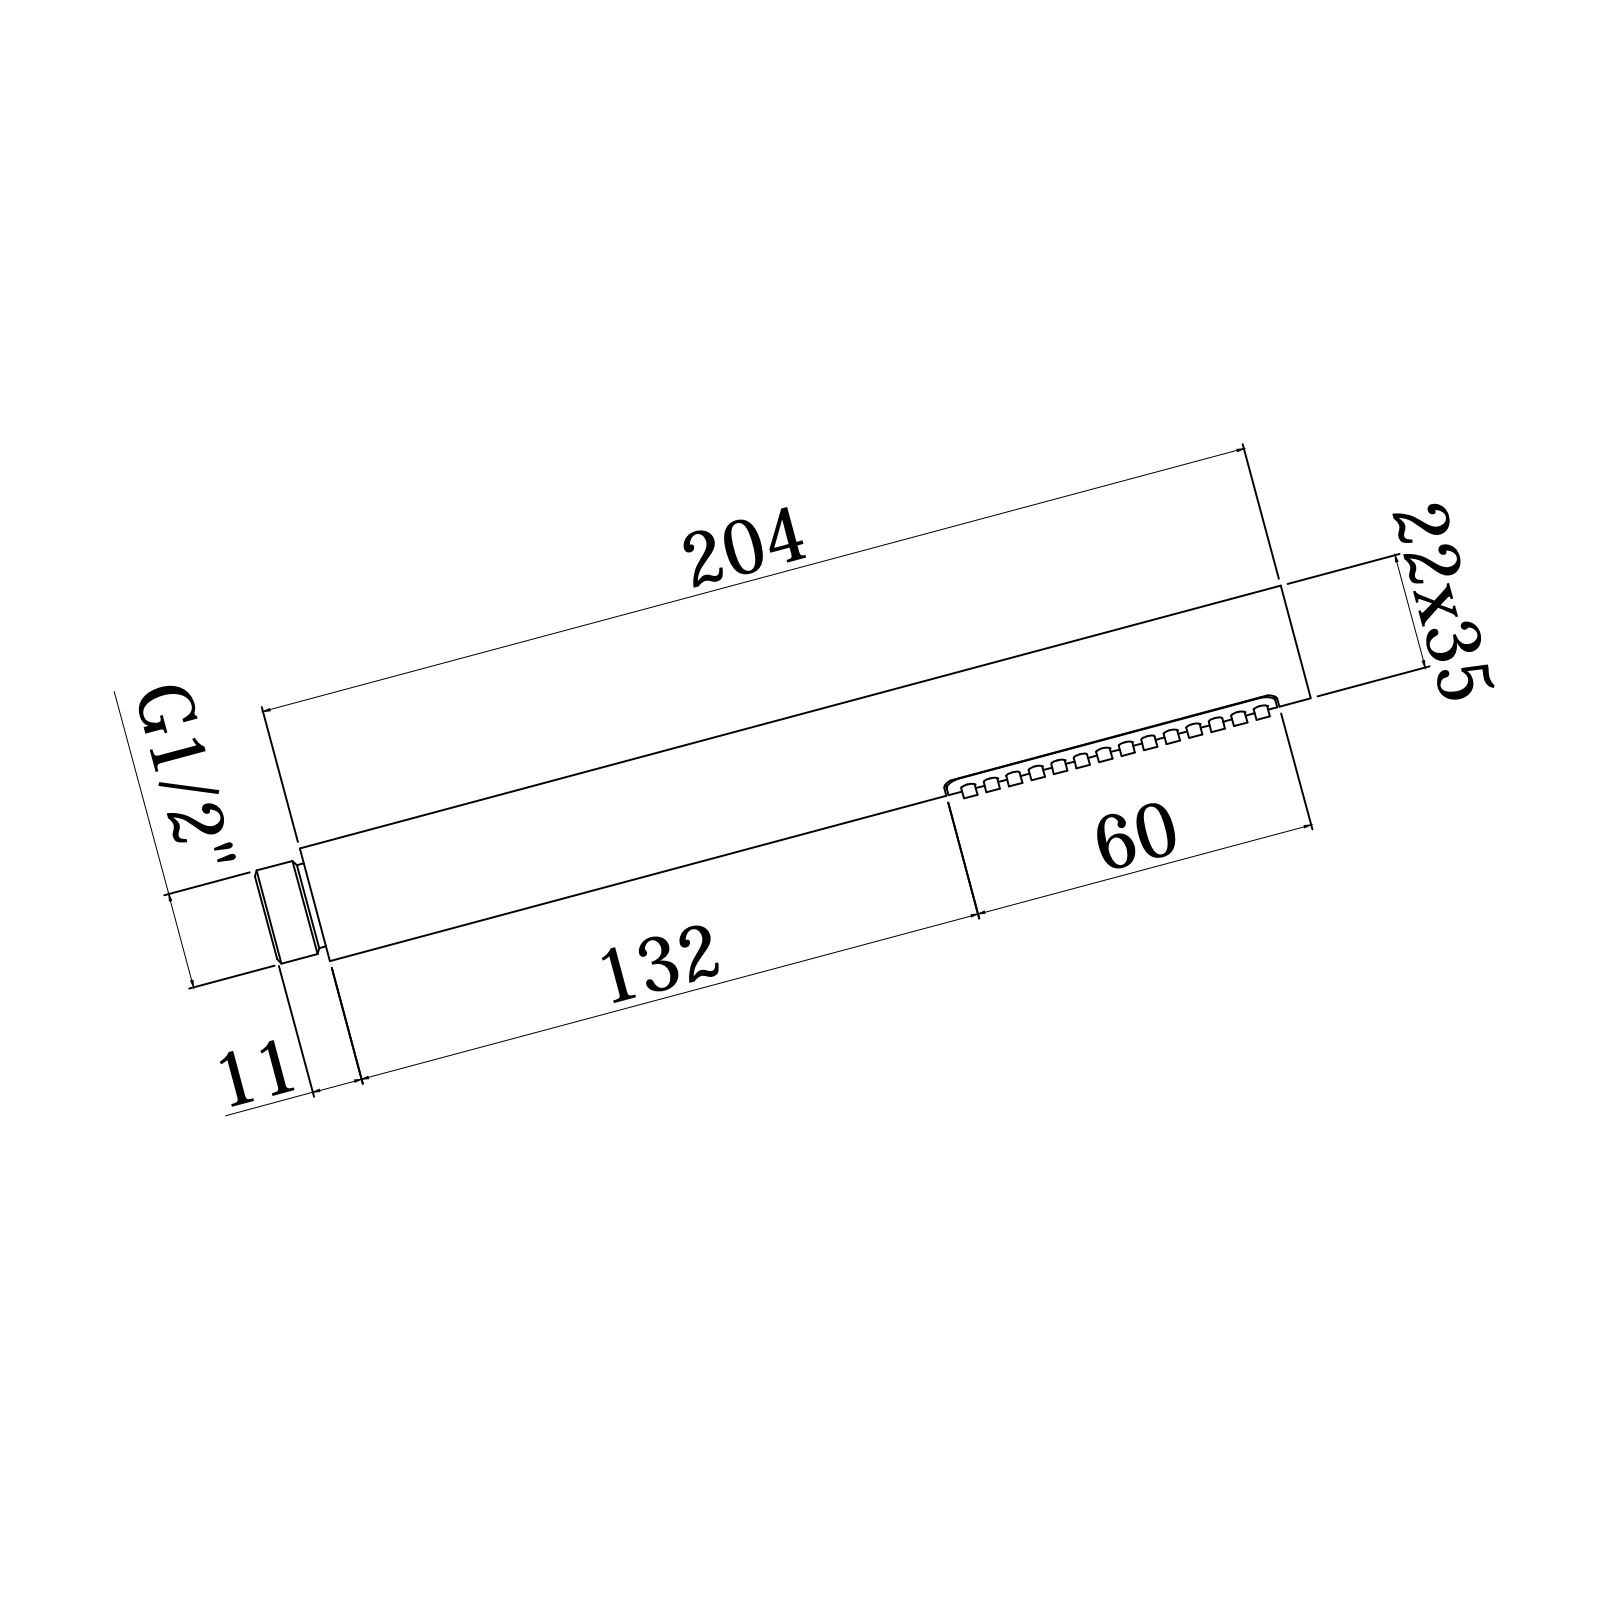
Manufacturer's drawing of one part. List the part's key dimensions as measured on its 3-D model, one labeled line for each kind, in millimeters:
Part name (STEP PRODUCT): ZDOC078CR
STEP written by: CREO PARAMETRIC BY PTC INC, 2020044 (CONFIG_CONTROL_DESIGN)
Units: millimetres
Bodies: 1 solid, 317 faces (5 planar, 206 cylindrical, 106 other)
Overall size (bounding box): 217 × 35 × 24
Volume: 128 044 mm³ · Surface area: 21 791 mm²
Round holes (diameter × count): ⌀1 ×50
Round bosses / shafts (diameter × count): ⌀2.5 ×50, ⌀21 ×1, ⌀20 ×1, ⌀18 ×1
Main face-to-face distances: 204, 13, 217, 1.5, 11.5, 205.5, 10, 3, 207
Hole centre spacings: 11.18, 5, 7.07, 10, 15.81, 20.62, 15, 25.5
